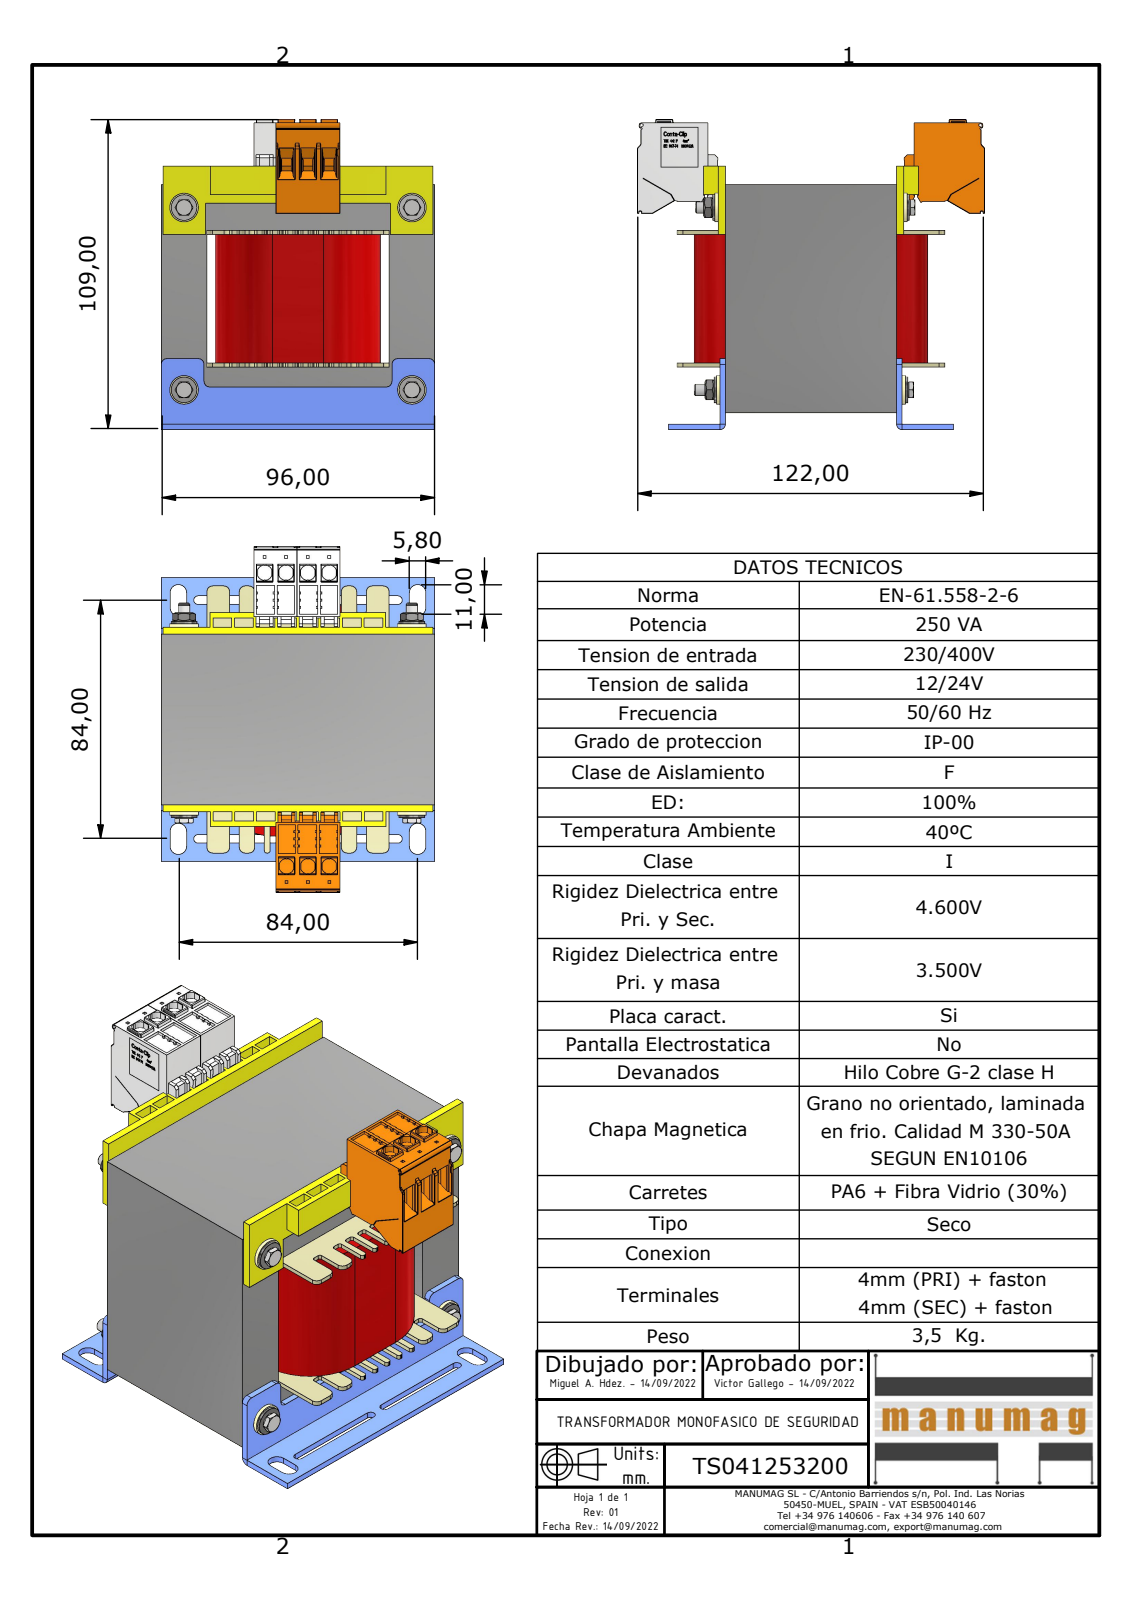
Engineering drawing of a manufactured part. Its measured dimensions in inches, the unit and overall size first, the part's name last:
Units: inches
Overall size (bounding box): 4.799 × 4.291 × 3.78
Round holes (diameter × count): ⌀0.128 ×4, ⌀0.157 ×4, ⌀0.169 ×4, ⌀0.217 ×4, ⌀0.228 ×2
Round bosses / shafts (diameter × count): ⌀0.394 ×4, ⌀0.354 ×4, ⌀0.216 ×4, ⌀0.193 ×4
Partial cylindrical surfaces — rounded edges, fillets, slot ends (radius × count): R0.006 ×271, R0.008 ×86, R0.031 ×52, R0.02 ×22, R0.079 ×22, R0.012 ×12, R0.039 ×8, R0.059 ×8
Main face-to-face distances: 2.52, 0.63, 1.26, 3.15, 1.89, 2.362, 0.079, 3.78, 0.118, 0.512
Hole centre spacings: 2.52, 3.15, 4.033
Volume: 33.11 in³ · Surface area: 216.3 in²
Bodies: 33 solids, 5986 faces (4782 planar, 833 cylindrical, 371 other)
Part name (STEP PRODUCT): TS041253200; EI96 x 80 - 60 (RC32); AF32DIN; EI 96 X 80 - 60 (+7 more)
STEP written by: Autodesk Inventor 2023 (AUTOMOTIVE_DESIGN)
